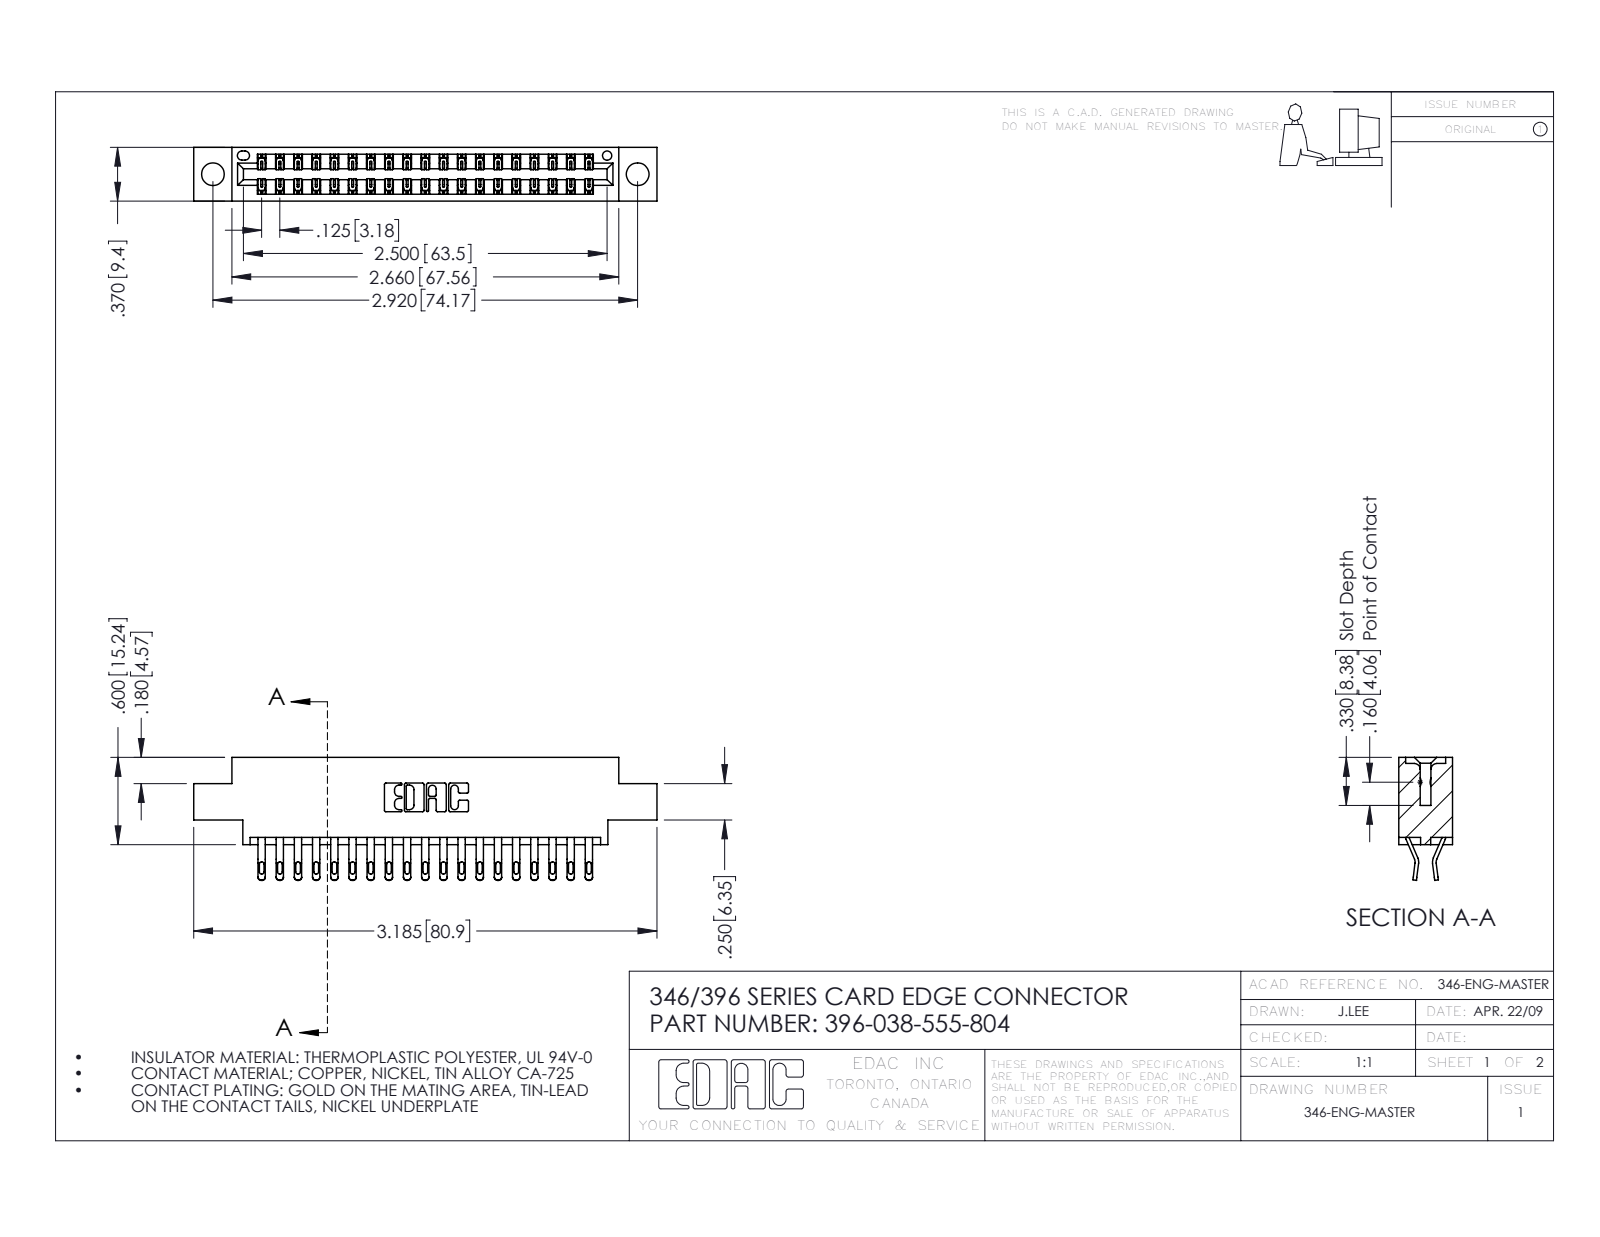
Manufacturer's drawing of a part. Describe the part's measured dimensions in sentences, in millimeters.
The part is named "345-292-001_555 Tail; 346 Part_0.170 Offset - 0.156 Dia-TH; 396-038-555-804". Its 3-D file was written by "SolidWorks 2016 (CONFIG_CONTROL_DESIGN)". It is 39 solids with 2330 faces: 1334 planar, 996 cylindrical and 0 other. Overall it measures 80.9 by 21.5 by 9.4 millimeters. Its volume is 7 570 cubic millimeters and its surface area 10 440 square millimeters. Round holes: 2 of diameter 4, 1 of diameter 1.6. Partial cylindrical surfaces (rounded edges, fillets, slot ends): 76 of radius 0.4, 76 of radius 0.5, 57 of radius 0.2, 22 of radius 0.3, 6 of radius 0.2, 6 of radius 0.8, 3 of radius 0.7, 2 of radius 0.3. The main face-to-face distances are 1.2, 8.2, 9.4, 6.4, 0.6, 1.8, 7.6, 7, 3.8, 5.6. The hole center spacings are 6.2, 68.9, 74.2.
